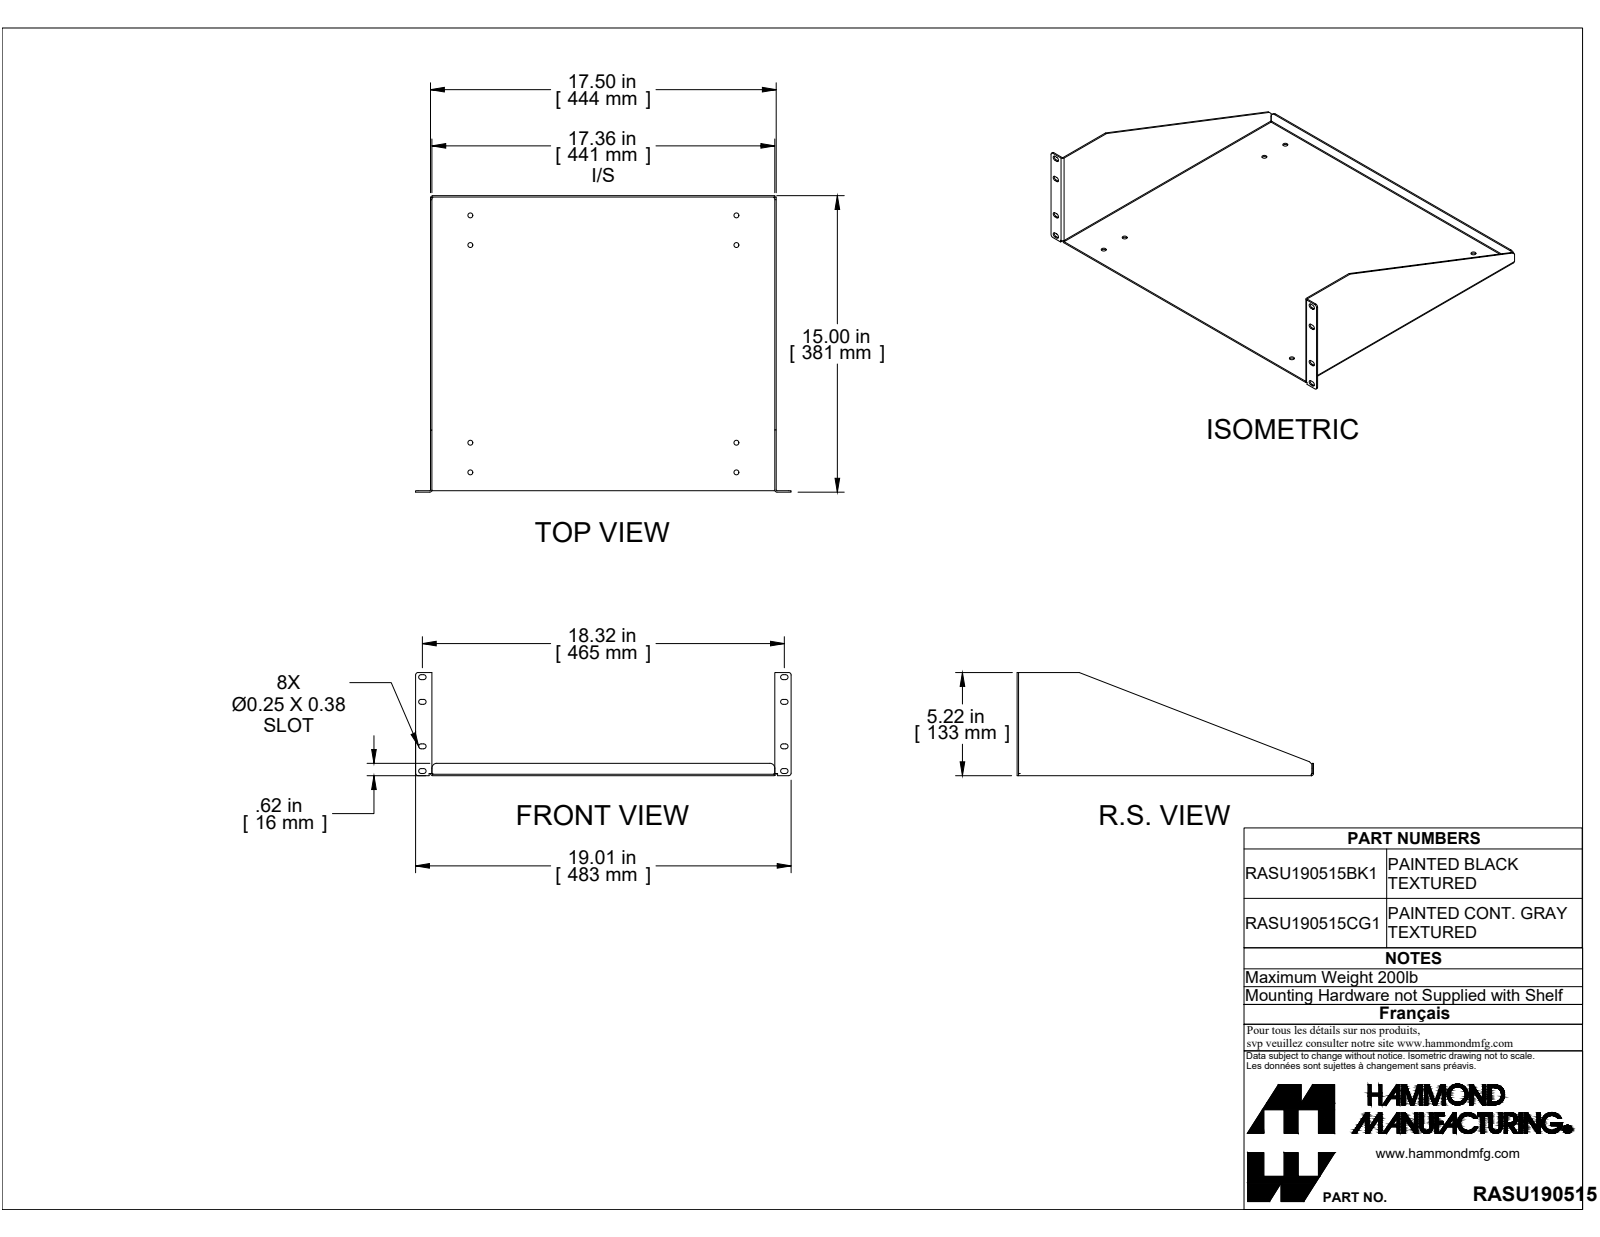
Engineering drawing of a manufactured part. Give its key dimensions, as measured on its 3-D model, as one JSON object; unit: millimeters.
{"part_name": "RASU190515BK1", "step_written_by": "SolidWorks 2019 (CONFIG_CONTROL_DESIGN)", "units": "millimeters", "bodies": {"solids": 1, "faces": 104, "planar": 56, "cylindrical": 44, "other": 4}, "overall_size": [482.8, 381, 132.5], "volume_mm3": 443300, "surface_area_mm2": 489200, "round_holes": [[6.4, 8]], "partial_cylinders_radius": [[3.2, 20], [0.9, 5], [2.7, 5], [1.4, 3], [6.4, 2]], "face_to_face_distances": [1.8, 442.7, 440.8, 444.5, 377.3, 379.2, 1.8, 379.2, 381, 15.9], "hole_center_spacings": [38.1, 292.1, 342.1, 344.2, 449.8, 254, 330.2, 426.1]}
